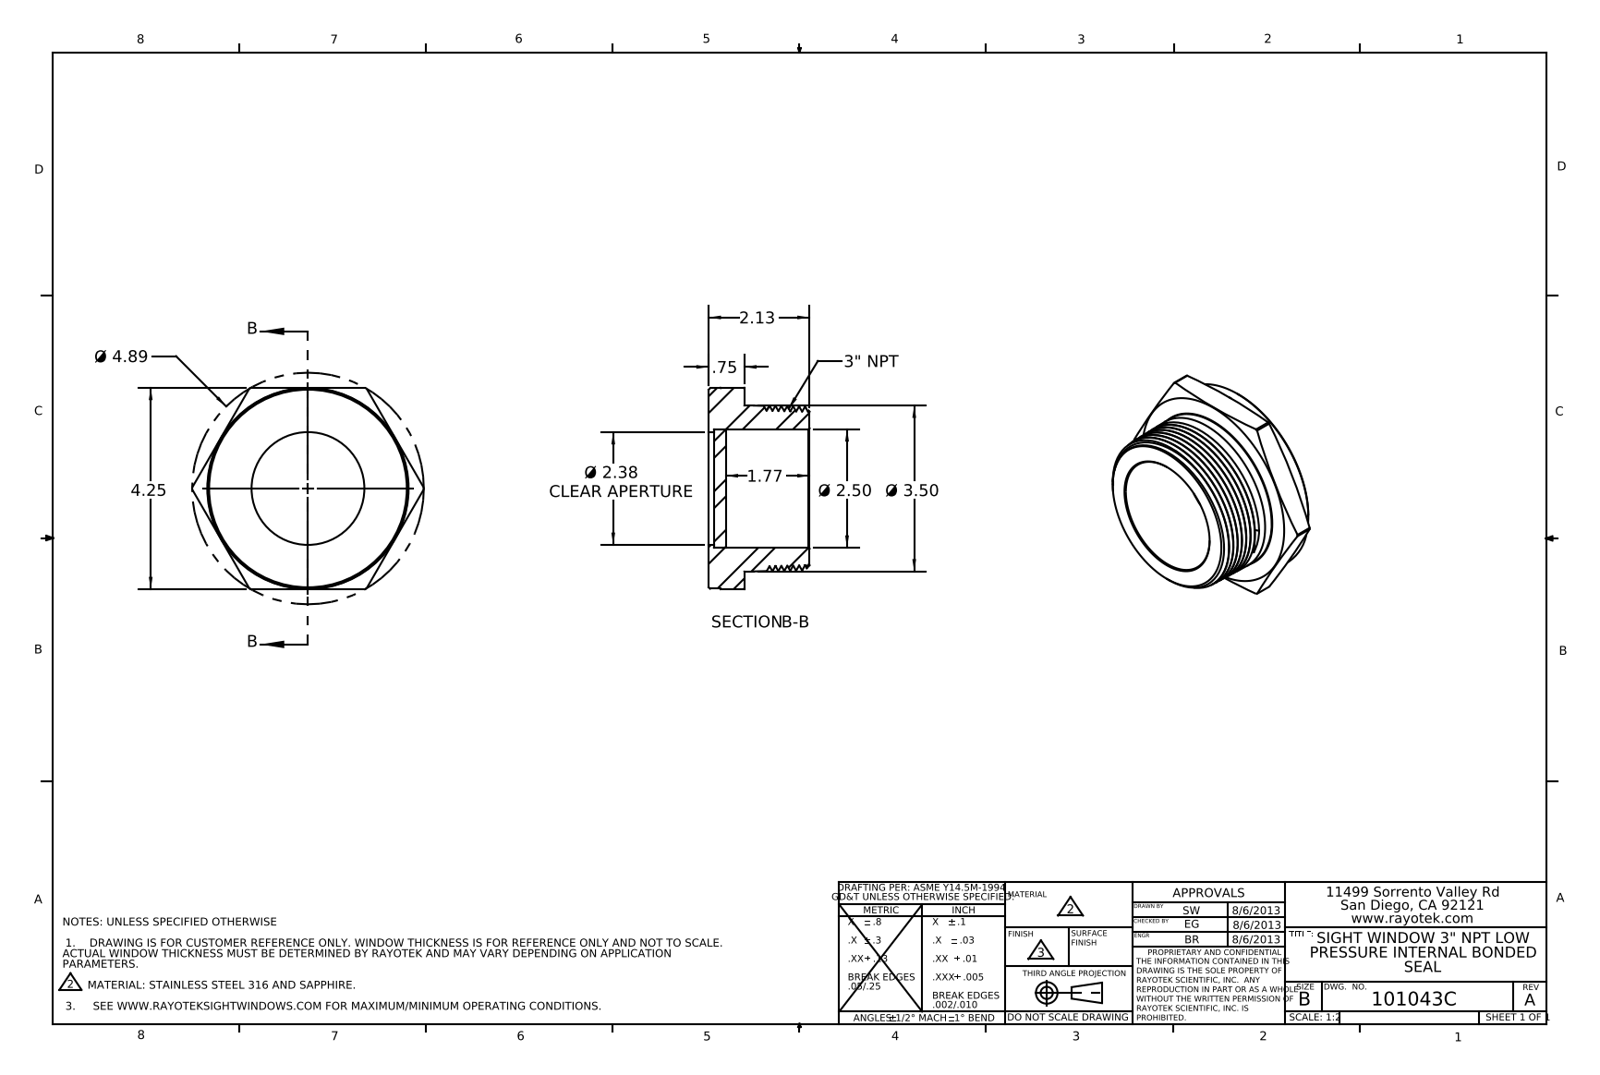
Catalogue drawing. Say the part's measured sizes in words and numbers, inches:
The part is named "403043". Its 3-D file was written by "SolidWorks 2012 (AUTOMOTIVE_DESIGN)". It is 2 solids with 65 faces: 15 planar, 17 cylindrical and 33 other. Overall it measures 4.887 by 4.25 by 2.13 inches. Its volume is 14.62 cubic inches and its surface area 82.51 square inches. Round holes: 1 of diameter 2.38, 1 of diameter 2.5. Round bosses or shafts: 1 of diameter 4.23, 1 of diameter 3.5. Partial cylindrical surfaces (rounded edges, fillets, slot ends): 1 of radius 2.444. The main face-to-face distances are 0.12, 0.36, 0.24, 0.75, 0.63, 0.39, 4.25, 2.13, 2.01, 1.77.
